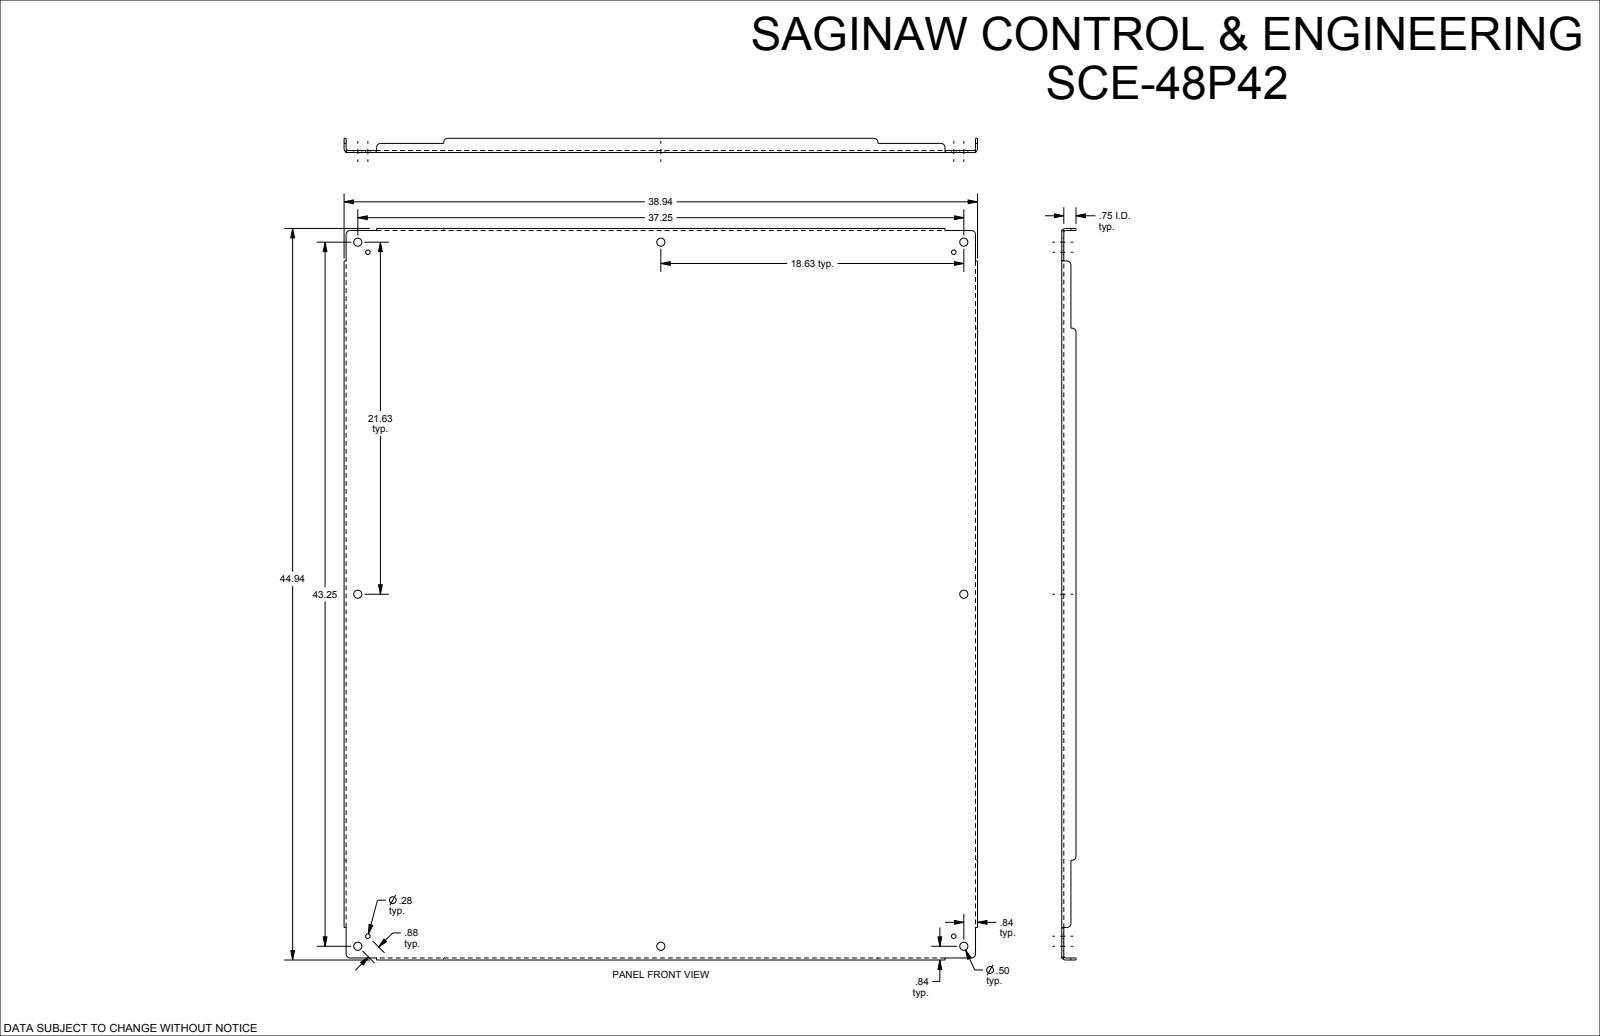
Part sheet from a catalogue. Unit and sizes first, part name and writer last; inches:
Units: inches
Overall size (bounding box): 44.938 × 38.938 × 0.875
Round holes (diameter × count): ⌀0.5 ×8, ⌀0.281 ×4
Partial cylindrical surfaces — rounded edges, fillets, slot ends (radius × count): R0.25 ×12, R0.112 ×4, R0.237 ×4
Main face-to-face distances: 0.125, 0.125, 38.813, 44.813, 38.687, 38.938, 44.687, 44.938, 0.75, 0.875
Hole centre spacings: 0.875, 18.017, 18.625, 21.015, 21.625, 28.54, 36.636, 42.227
Volume: 229.7 in³ · Surface area: 3 699 in²
Bodies: 1 solid, 110 faces (46 planar, 40 cylindrical, 24 other)
Part name (STEP PRODUCT): SCE-48P42
STEP written by: SolidWorks 2019 (CONFIG_CONTROL_DESIGN)
